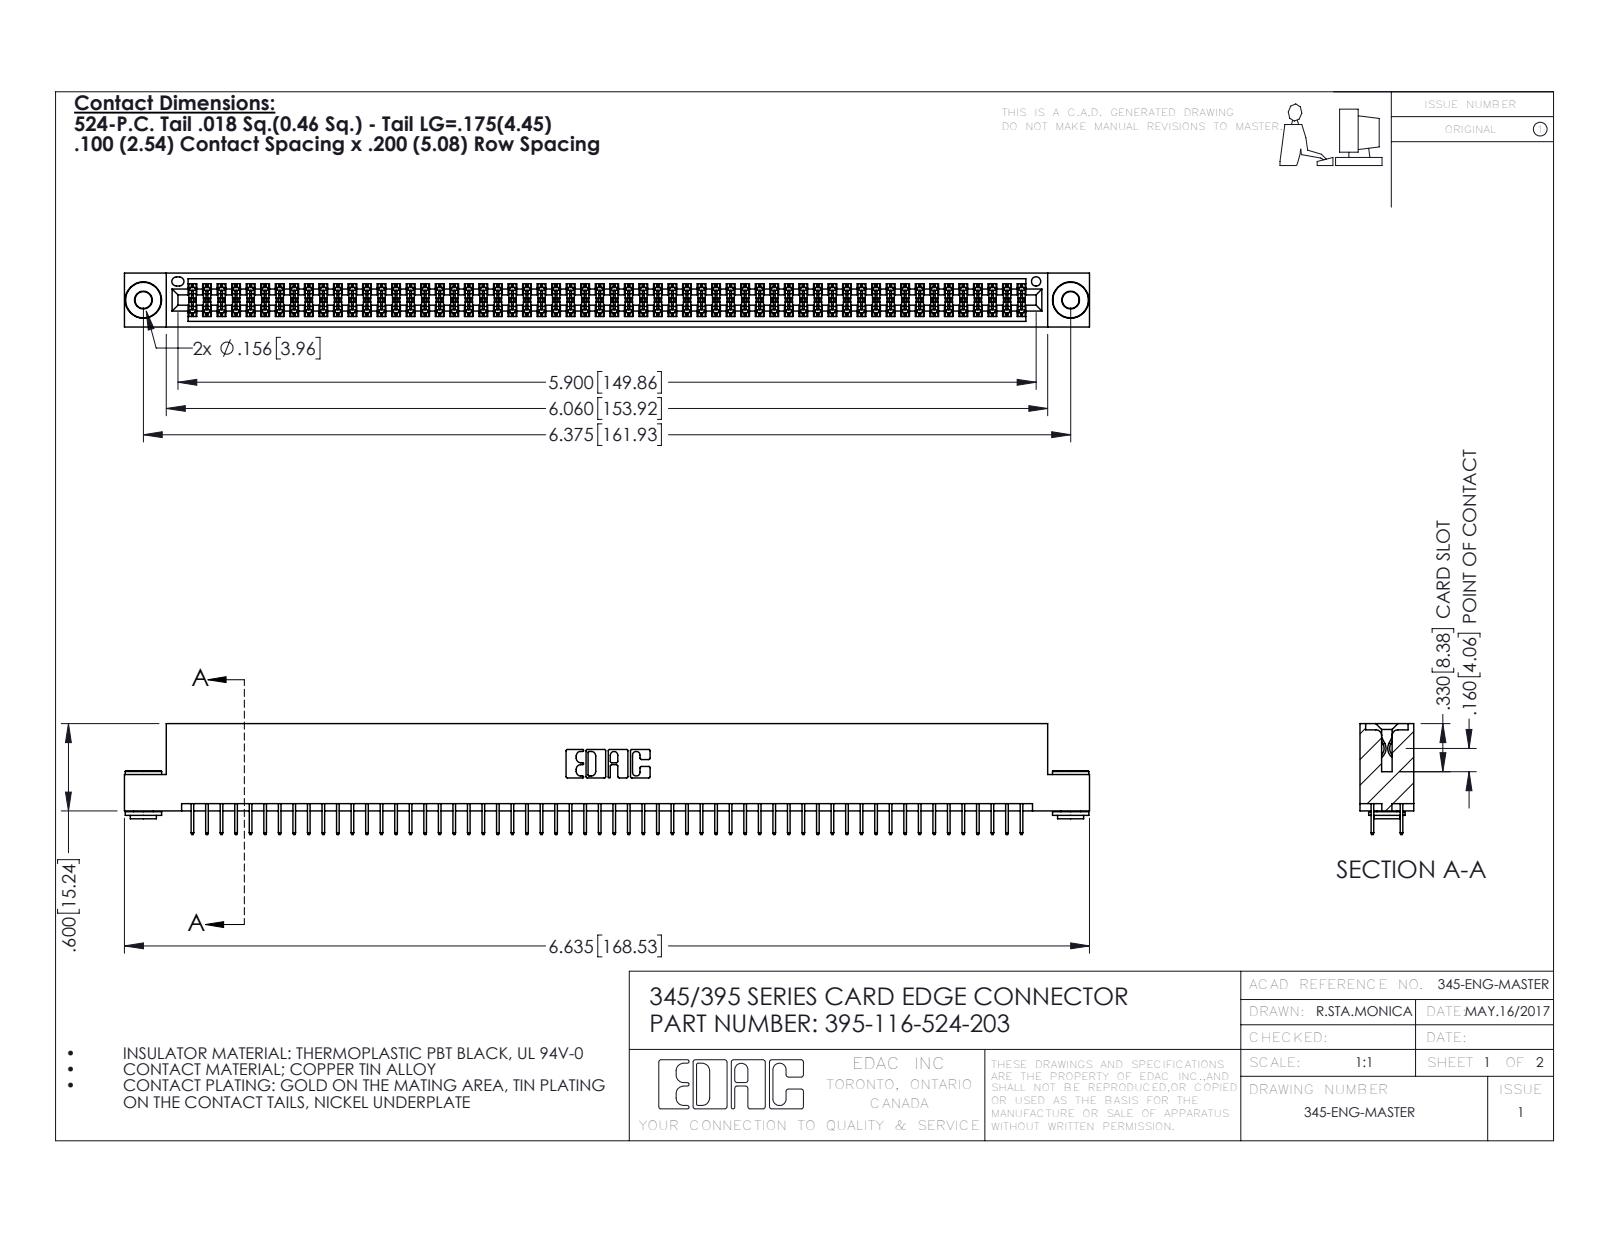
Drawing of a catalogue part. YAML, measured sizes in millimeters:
part_name: "345-250-002_345-250-002-102; 395-116-524-203; 345 Part_Flush Mounting Lugs - 0.156 Dia-TH; 345-292-001_345-293-124"
step_written_by: "SolidWorks 2016 (CONFIG_CONTROL_DESIGN)"
units: millimeters
bodies: {solids: 119, faces: 6428, planar: 4614, cylindrical: 1806, other: 8}
overall_size: [168.5, 19.4, 9.4]
volume: 16400
surface_area: 24240
round_holes:
  - {diameter: 2.9, count: 2}
  - {diameter: 4, count: 2}
  - {diameter: 1.6, count: 1}
round_bosses_or_shafts:
  - {diameter: 6.4, count: 2}
  - {diameter: 4.6, count: 2}
  - {diameter: 3.5, count: 2}
partial_cylinders:
  - {radius: 0.2, count: 174}
  - {radius: 0.3, count: 22}
  - {radius: 0.2, count: 6}
  - {radius: 0.8, count: 6}
  - {radius: 0.7, count: 3}
  - {radius: 0.4, count: 2}
  - {radius: 0.5, count: 2}
  - {radius: 0.6, count: 2}
face_to_face_distances: [1.8, 7.6, 5.1, 9.4, 0.6, 2.5, 6.9, 5.7, 1.8, 4.4]
hole_center_spacings: [6.9, 155.9, 161.9]
